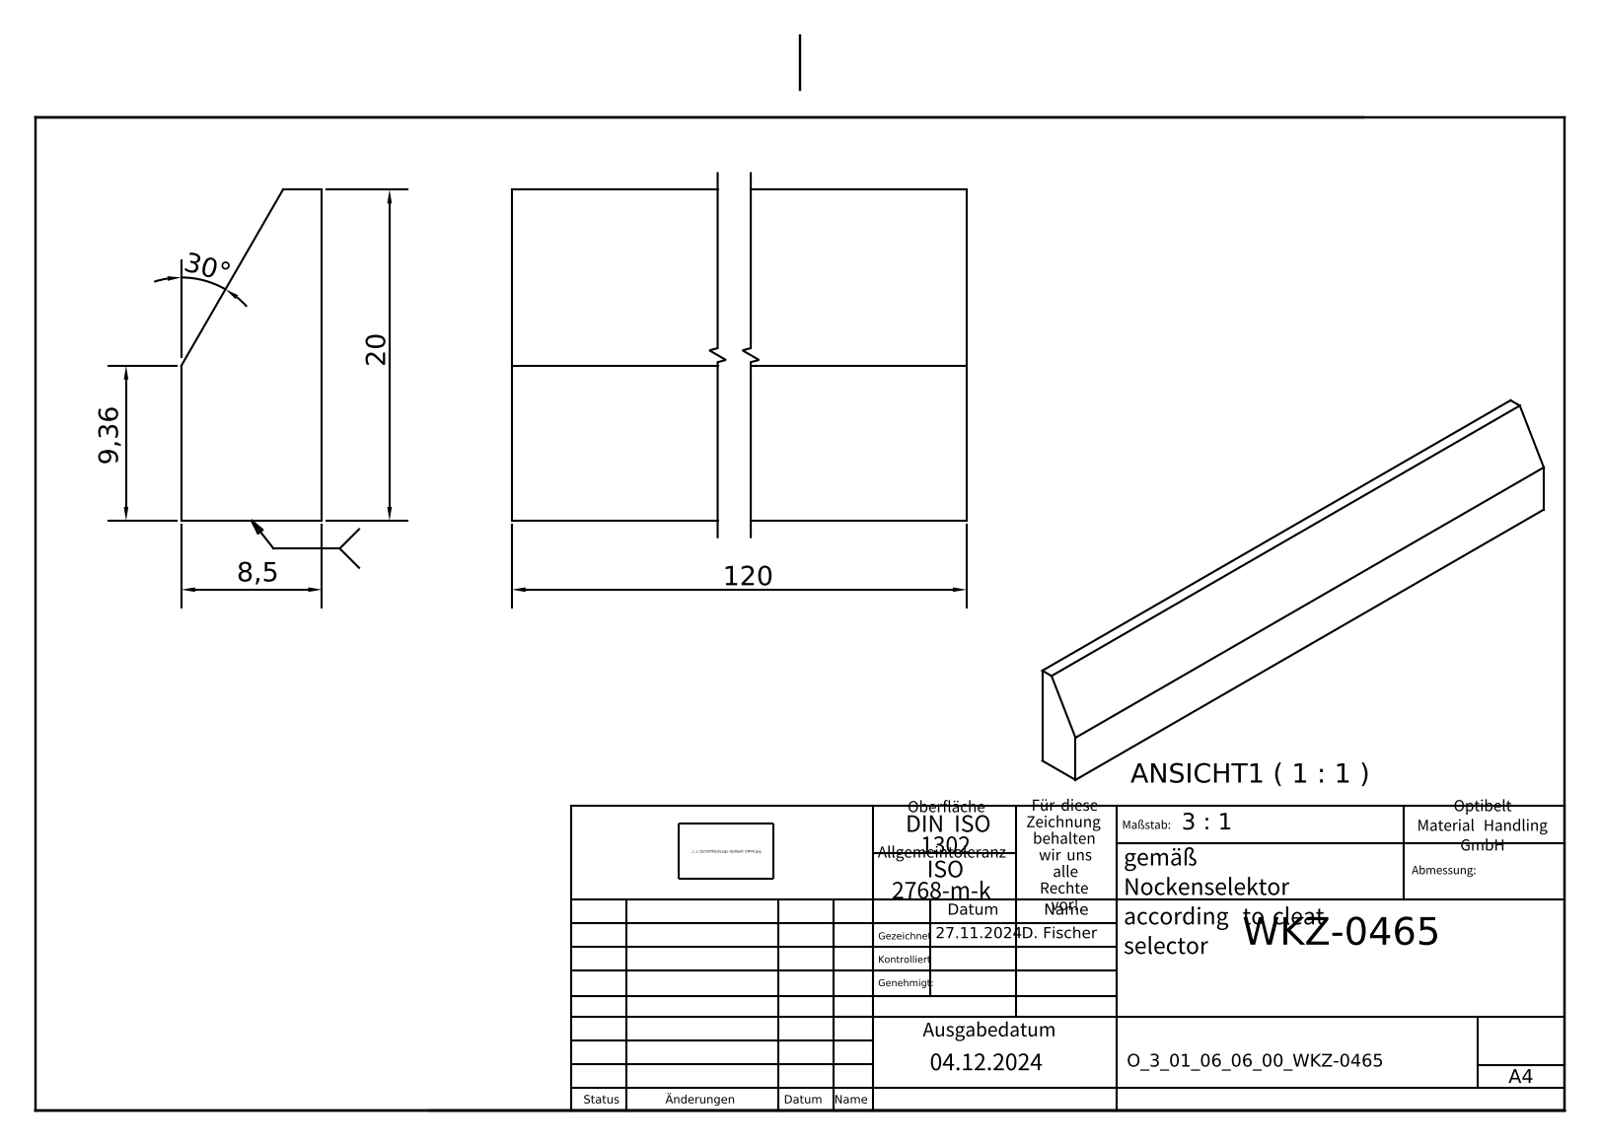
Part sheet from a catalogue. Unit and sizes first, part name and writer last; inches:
Units: inches
Overall size (bounding box): 4.724 × 0.787 × 0.335
Main face-to-face distances: 0.335, 0.787, 4.724
Volume: 1.006 in³ · Surface area: 10.19 in²
Bodies: 1 solid, 7 faces (7 planar, 0 cylindrical, 0 other)
Part name (STEP PRODUCT): O_3_01_06_06_00_WKZ-0465
STEP written by: Autodesk Inventor 2025 (AUTOMOTIVE_DESIGN)
